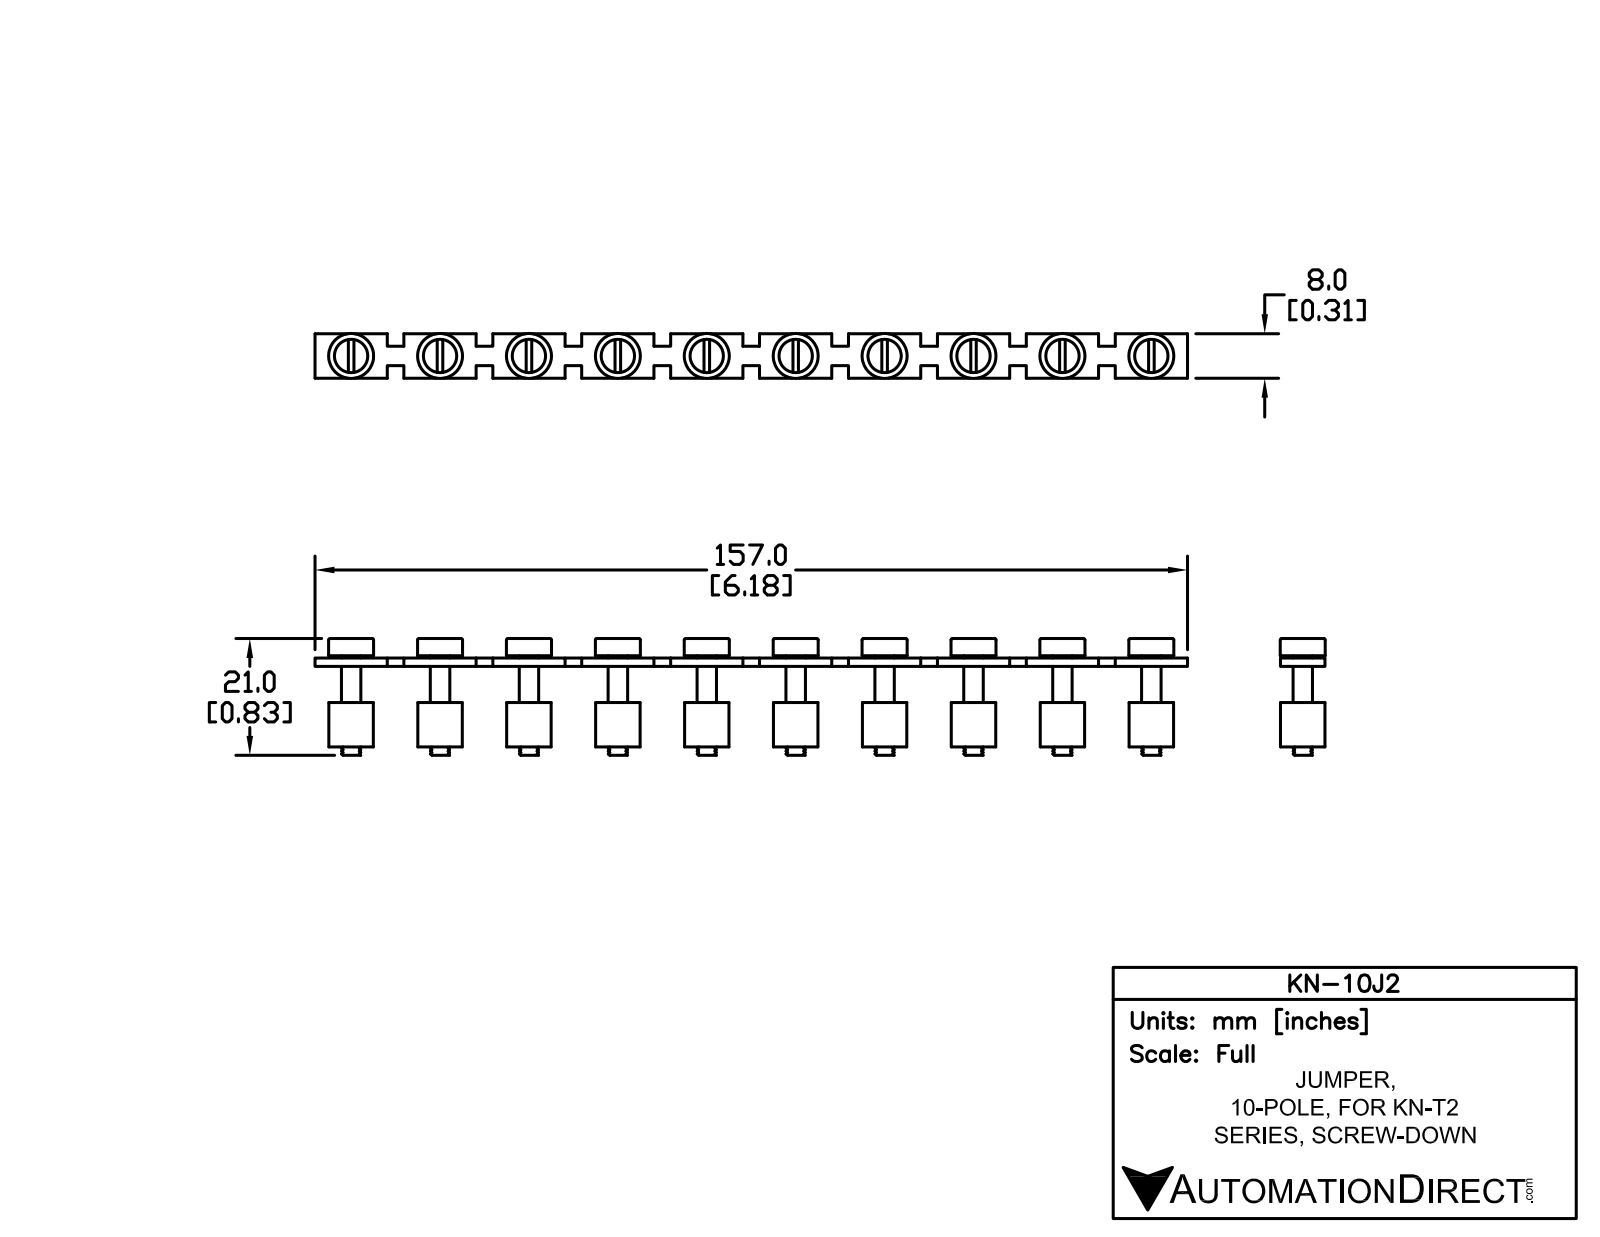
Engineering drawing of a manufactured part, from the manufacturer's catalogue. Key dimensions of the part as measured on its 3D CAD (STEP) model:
Part name (STEP PRODUCT): KN-10J2
STEP written by: SolidWorks 2014 (AUTOMOTIVE_DESIGN)
Units: millimetres
Bodies: 31 solids, 418 faces (208 planar, 150 cylindrical, 60 other)
Overall size (bounding box): 157 × 21 × 8.1
Volume: 7 335 mm³ · Surface area: 12 087 mm²
Round holes (diameter × count): ⌀4.5 ×10, ⌀6 ×10
Round bosses / shafts (diameter × count): ⌀8.1 ×10, ⌀8 ×10, ⌀6.75 ×10, ⌀3.5 ×10
Main face-to-face distances: 1.5, 8, 16, 3, 0.5, 19, 14.5, 6.5, 2, 11
Hole centre spacings: 16, 32, 48, 64, 80, 96, 112, 128
